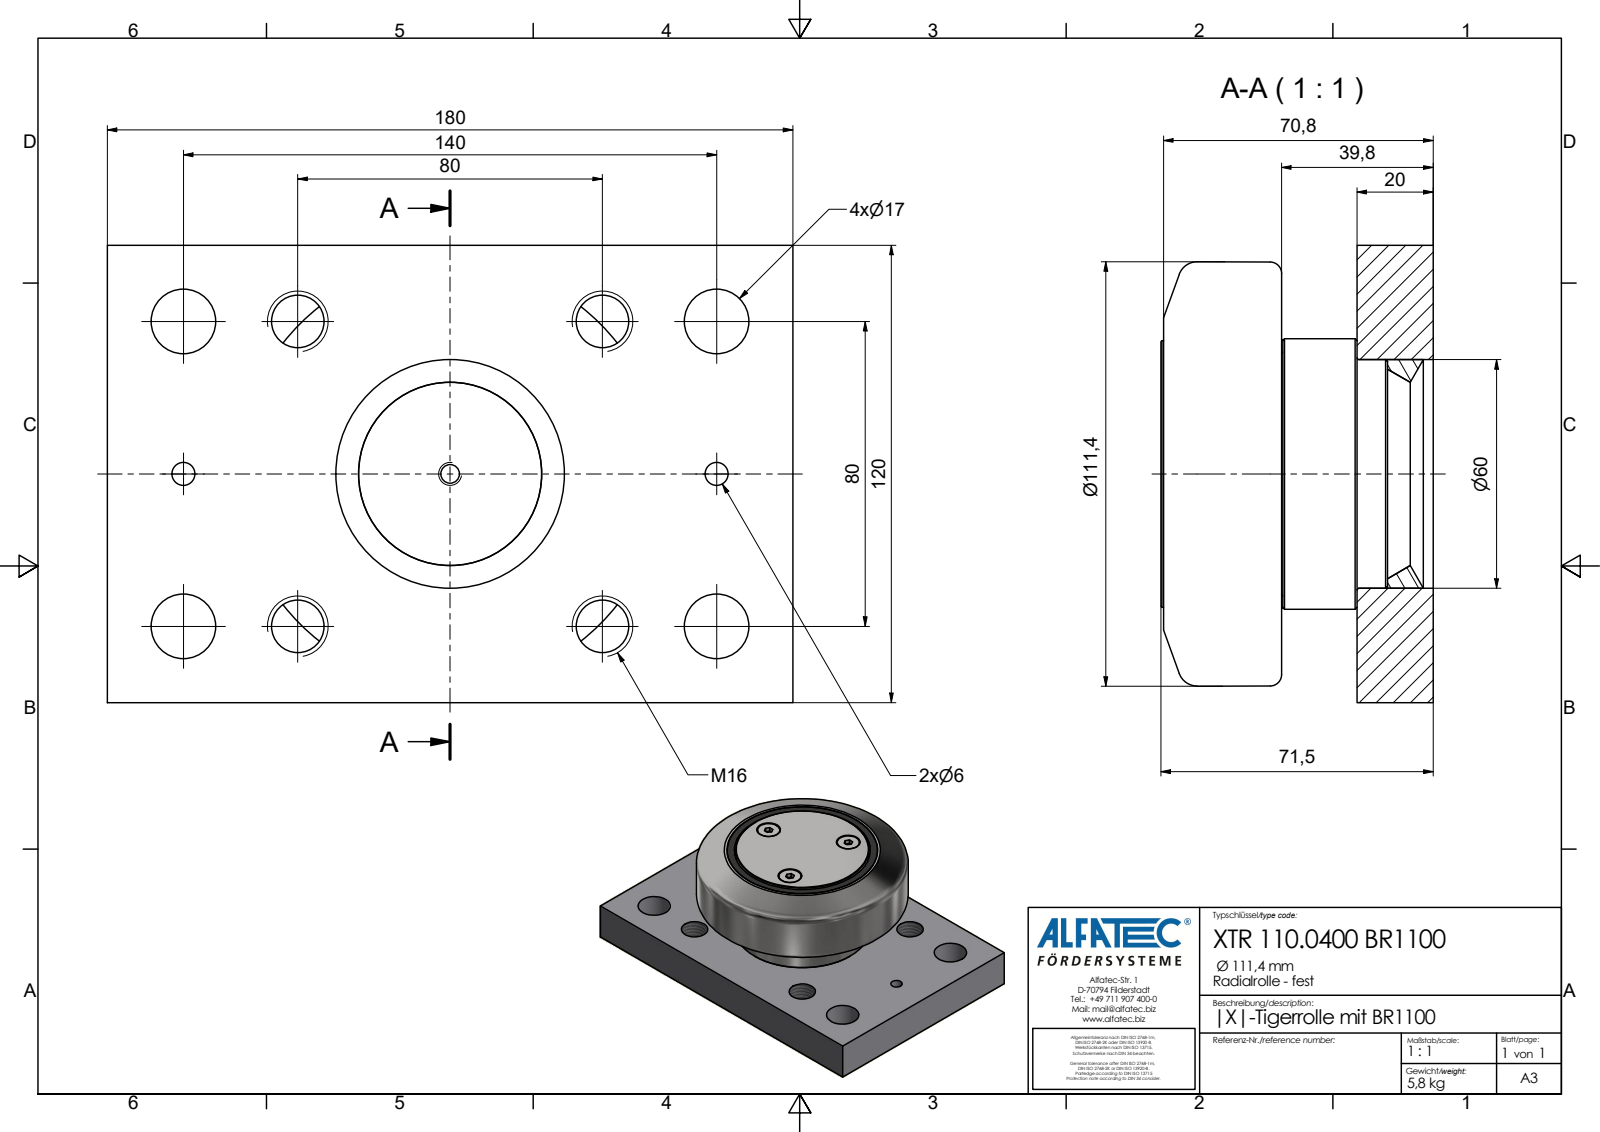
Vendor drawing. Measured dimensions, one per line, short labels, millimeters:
name: XTR 110.0400 BR1100_Kontur
written by: Autodesk Inventor 2020 (AP242_MANAGED_MODEL_BASED_3D_ENGINEERING_MIM_LF)
unit: mm
bodies: 1 solid, 63 faces (37 planar, 19 cylindrical, 7 other)
size: 180 × 120 × 71.5
volume: 769 499 mm³; area: 85 595 mm²
holes: 4× ⌀13.84, 4× ⌀17, 3× ⌀12.4, 2× ⌀6
bosses: 3× ⌀11.7, 1× ⌀71, 1× ⌀70.5, 1× ⌀70
face distances: 20, 39.8, 19.8, 120, 71.5, 51.5, 31.7, 180, 70.8, 50.8
hole spacings: 80, 30, 40, 50, 85.44, 110, 117.05, 136.01
